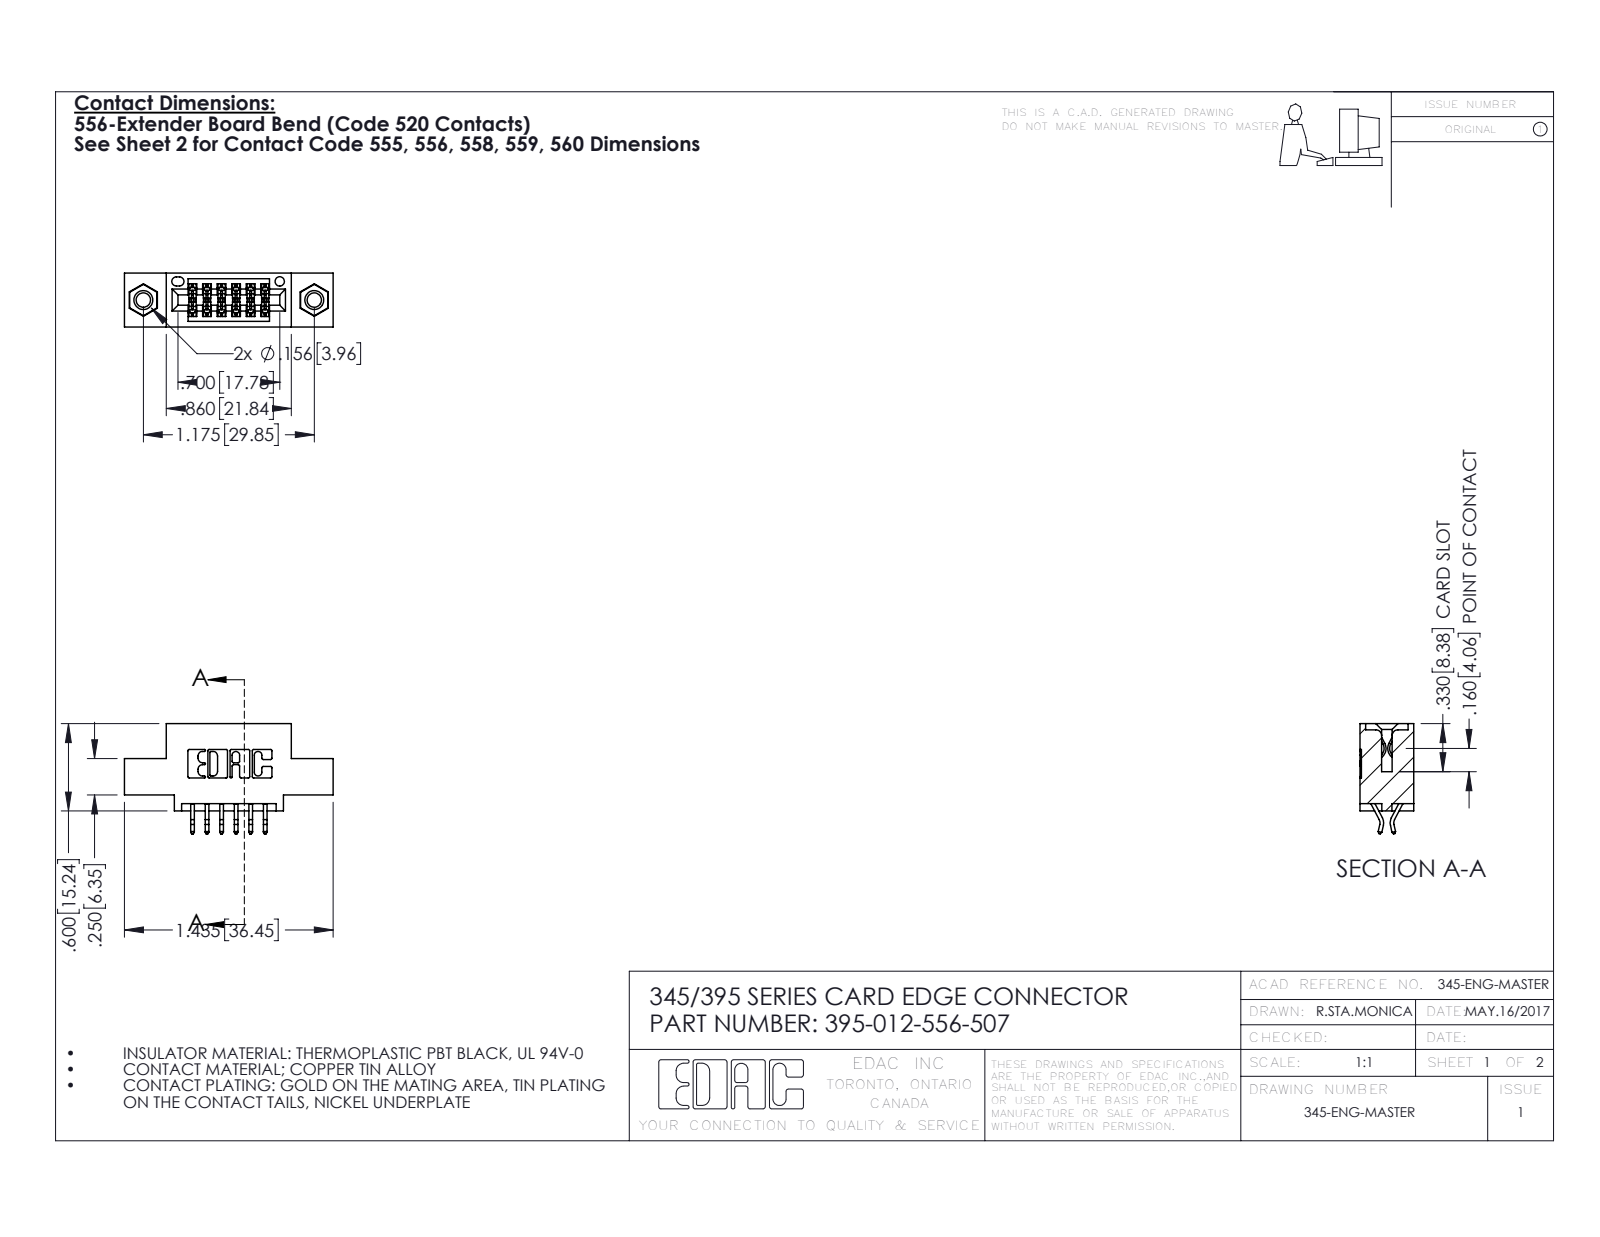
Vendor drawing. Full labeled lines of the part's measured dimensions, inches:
Part name (STEP PRODUCT): 345-292-001_556 Tail; 345-250-001_345-250-005-103; 395-012-556-507; 345 Part_0.110 Offset - 0.156 Dia-TI
STEP written by: SolidWorks 2016 (CONFIG_CONTROL_DESIGN)
Units: inches
Bodies: 15 solids, 862 faces (560 planar, 286 cylindrical, 16 other)
Overall size (bounding box): 1.435 × 0.757 × 0.37
Volume: 0.19 in³ · Surface area: 6.237 in²
Round holes (diameter × count): ⌀0.098 ×2, ⌀0.125 ×2, ⌀0.156 ×2, ⌀0.064 ×1
Round bosses / shafts (diameter × count): ⌀0.155 ×2
Partial cylindrical surfaces — rounded edges, fillets, slot ends (radius × count): R0.01 ×22, R0.006 ×18, R0.007 ×6, R0.031 ×6, R0.026 ×3, R0.01 ×2, R0.014 ×2, R0.019 ×2
Main face-to-face distances: 0.2, 0.37, 0.072, 0.298, 0.1, 0.025, 0.098, 0.272, 0.16, 0.06
Hole centre spacings: 0.27, 0.946, 1.175
